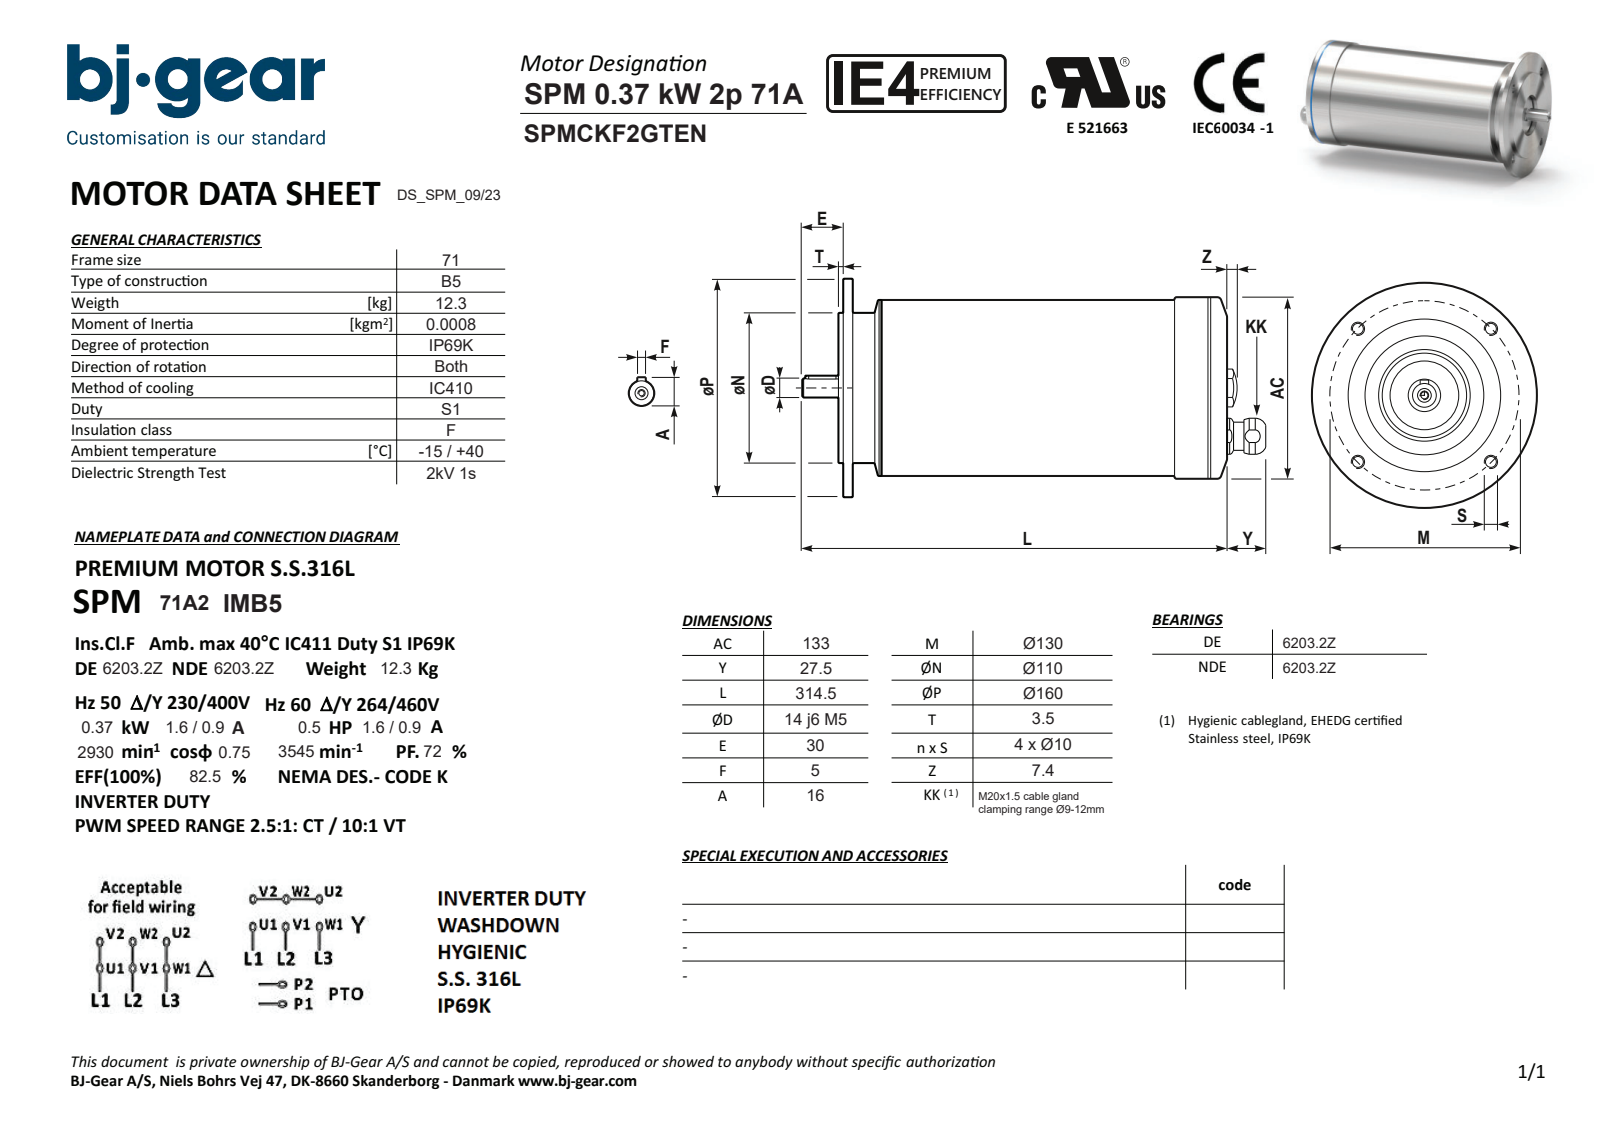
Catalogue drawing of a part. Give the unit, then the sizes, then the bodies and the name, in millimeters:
Units: millimetres
Overall size (bounding box): 342 × 160 × 160
Round holes (diameter × count): ⌀10 ×4, ⌀4.13 ×1, ⌀5.3 ×1, ⌀7 ×1, ⌀13.4 ×1, ⌀52 ×1
Round bosses / shafts (diameter × count): ⌀160 ×1, ⌀133 ×1, ⌀132.98 ×1, ⌀129 ×1, ⌀128.98 ×1, ⌀110 ×1, ⌀20 ×1, ⌀17 ×1
Partial cylindrical surfaces — rounded edges, fillets, slot ends (radius × count): R2.5 ×2, R12.8 ×1
Main face-to-face distances: 7, 277.5, 284.5, 288, 10.5, 3.5, 279, 1.5, 5.5, 9
Hole centre spacings: 65, 91.92, 47.49, 92.23, 129.99, 34
Volume: 3 756 000 mm³ · Surface area: 167 604 mm²
Bodies: 1 solid, 86 faces (31 planar, 30 cylindrical, 25 other)
Part name (STEP PRODUCT): SPMCKF2GTENN4KSA1-N---NNN
STEP written by: Solid Edge (AUTOMOTIVE_DESIGN)
